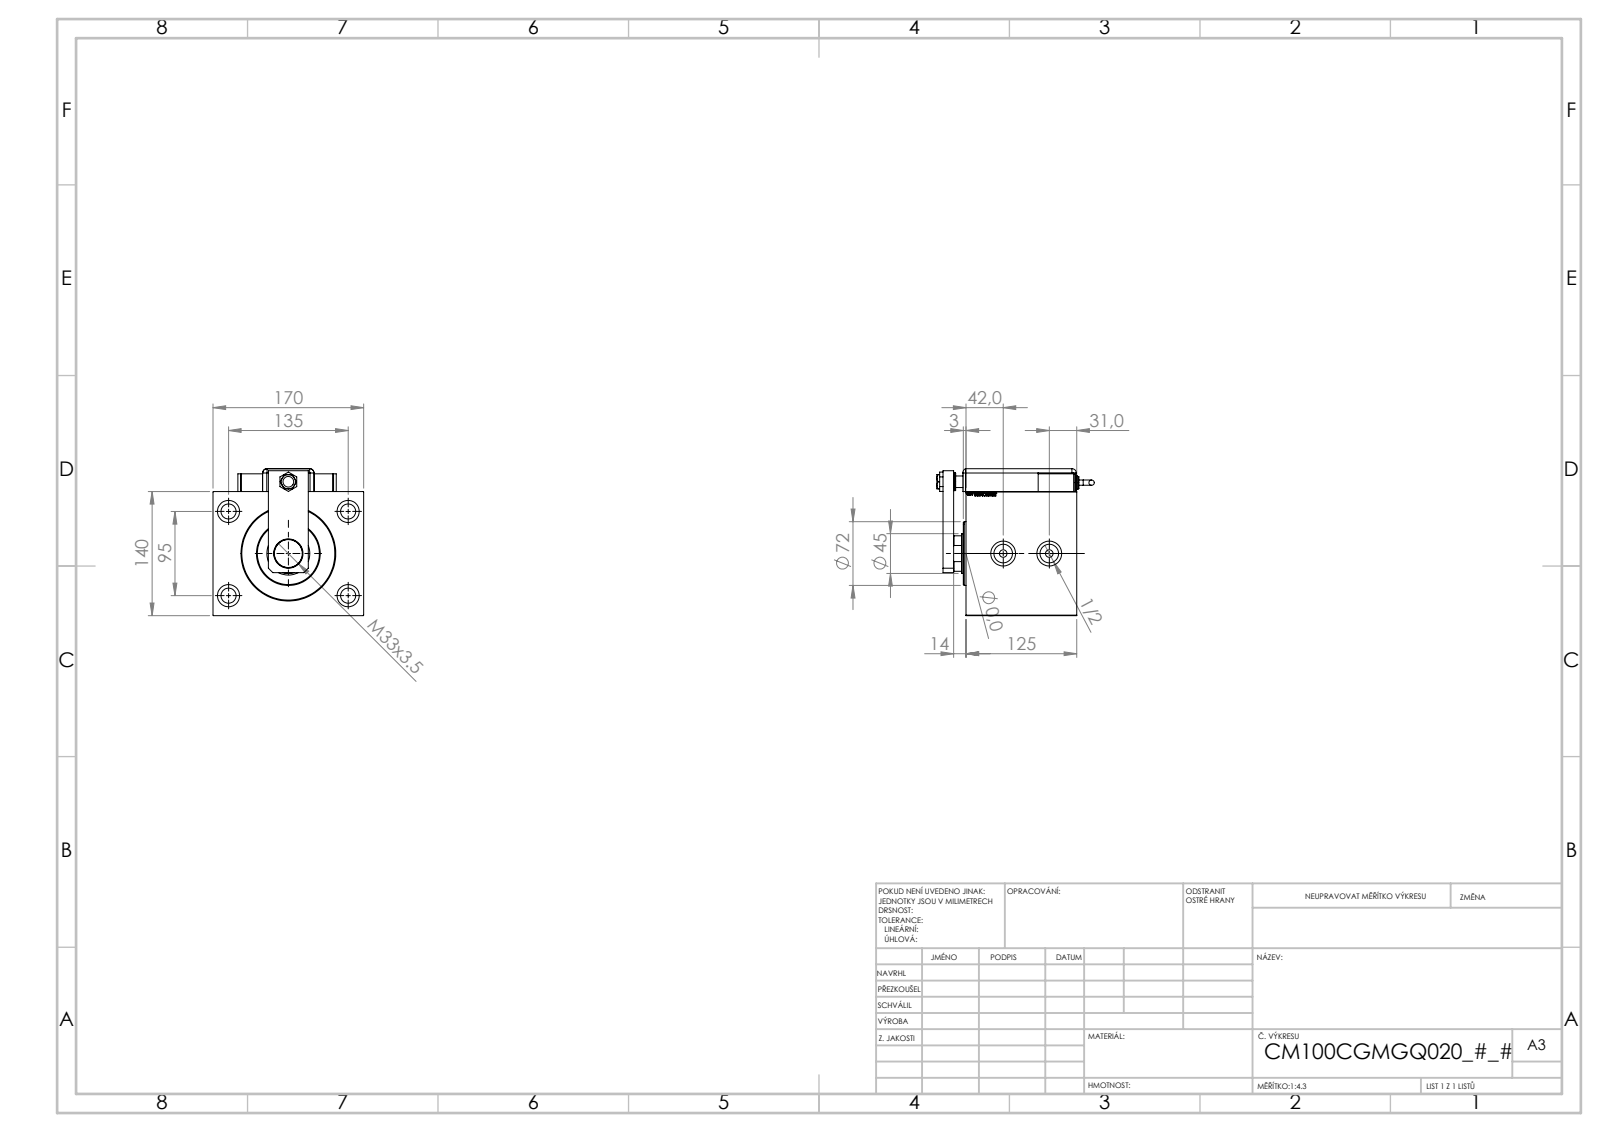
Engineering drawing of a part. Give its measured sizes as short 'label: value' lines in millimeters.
name: SWITCH_Q_FRONT_BACK; TYC; SWITCH Q; ZARAZKA_Q (+7 more)
written by: SolidWorks 2019 (CONFIG_CONTROL_DESIGN)
unit: mm
bodies: 13 solids, 1250 faces (616 planar, 117 cylindrical, 517 other)
size: 177.66 × 170 × 165.8
volume: 2 933 000 mm³; area: 299 140 mm²
holes: 4× ⌀17, 4× ⌀25, 2× ⌀4, 2× ⌀8, 2× ⌀8.5, 2× ⌀20.96, 2× ⌀28, 1× ⌀12, 1× ⌀13, 1× ⌀14, 1× ⌀31.5, 1× ⌀33
bosses: 3× ⌀20, 2× ⌀16, 2× ⌀14, 2× ⌀6, 1× ⌀72
rounds: 9× R5, 1× R10, 1× R22
face distances: 140, 125, 170, 74, 51, 3, 10, 21.6, 29.4, 103.4
hole spacings: 82.54, 75.36, 95, 135, 145.15, 165.08, 20, 52
